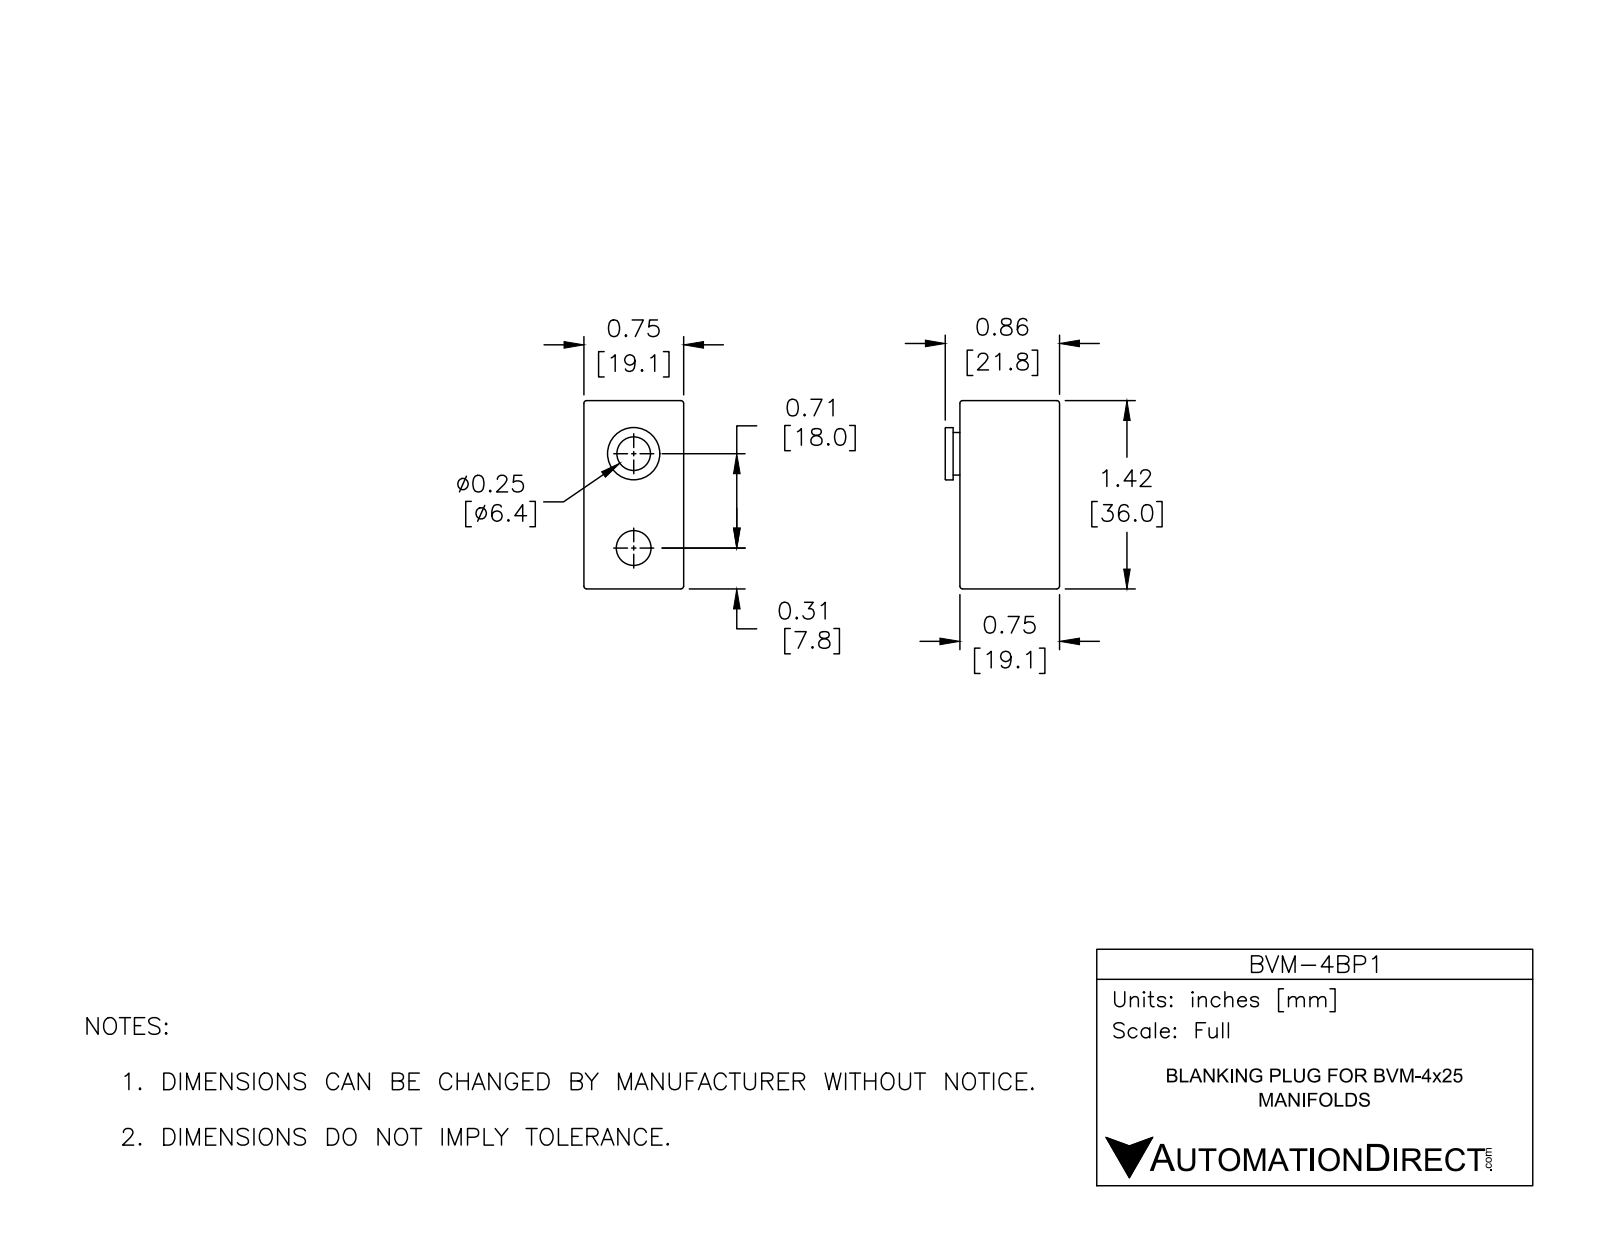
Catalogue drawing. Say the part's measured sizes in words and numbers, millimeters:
The part is named "BVM-4BP1". Its 3-D file was written by "SolidWorks 2016 (AUTOMOTIVE_DESIGN)". It is 1 solid with 61 faces: 11 planar, 28 cylindrical and 22 other. Overall it measures 36 by 21.8 by 19.1 millimeters. Its volume is 11 700 cubic millimeters and its surface area 4 434 square millimeters. Round holes: 2 of diameter 6.6, 1 of diameter 6.4, 1 of diameter 7.9, 1 of diameter 10.8. Round bosses or shafts: 1 of diameter 10, 1 of diameter 8.1. Partial cylindrical surfaces (rounded edges, fillets, slot ends): 12 of radius 0.5. The main face-to-face distances are 19.1, 36, 12.9, 6.1, 9.4, 3.5, 9.7, 20.3, 10.9, 7.4. The hole center spacings are 18.
